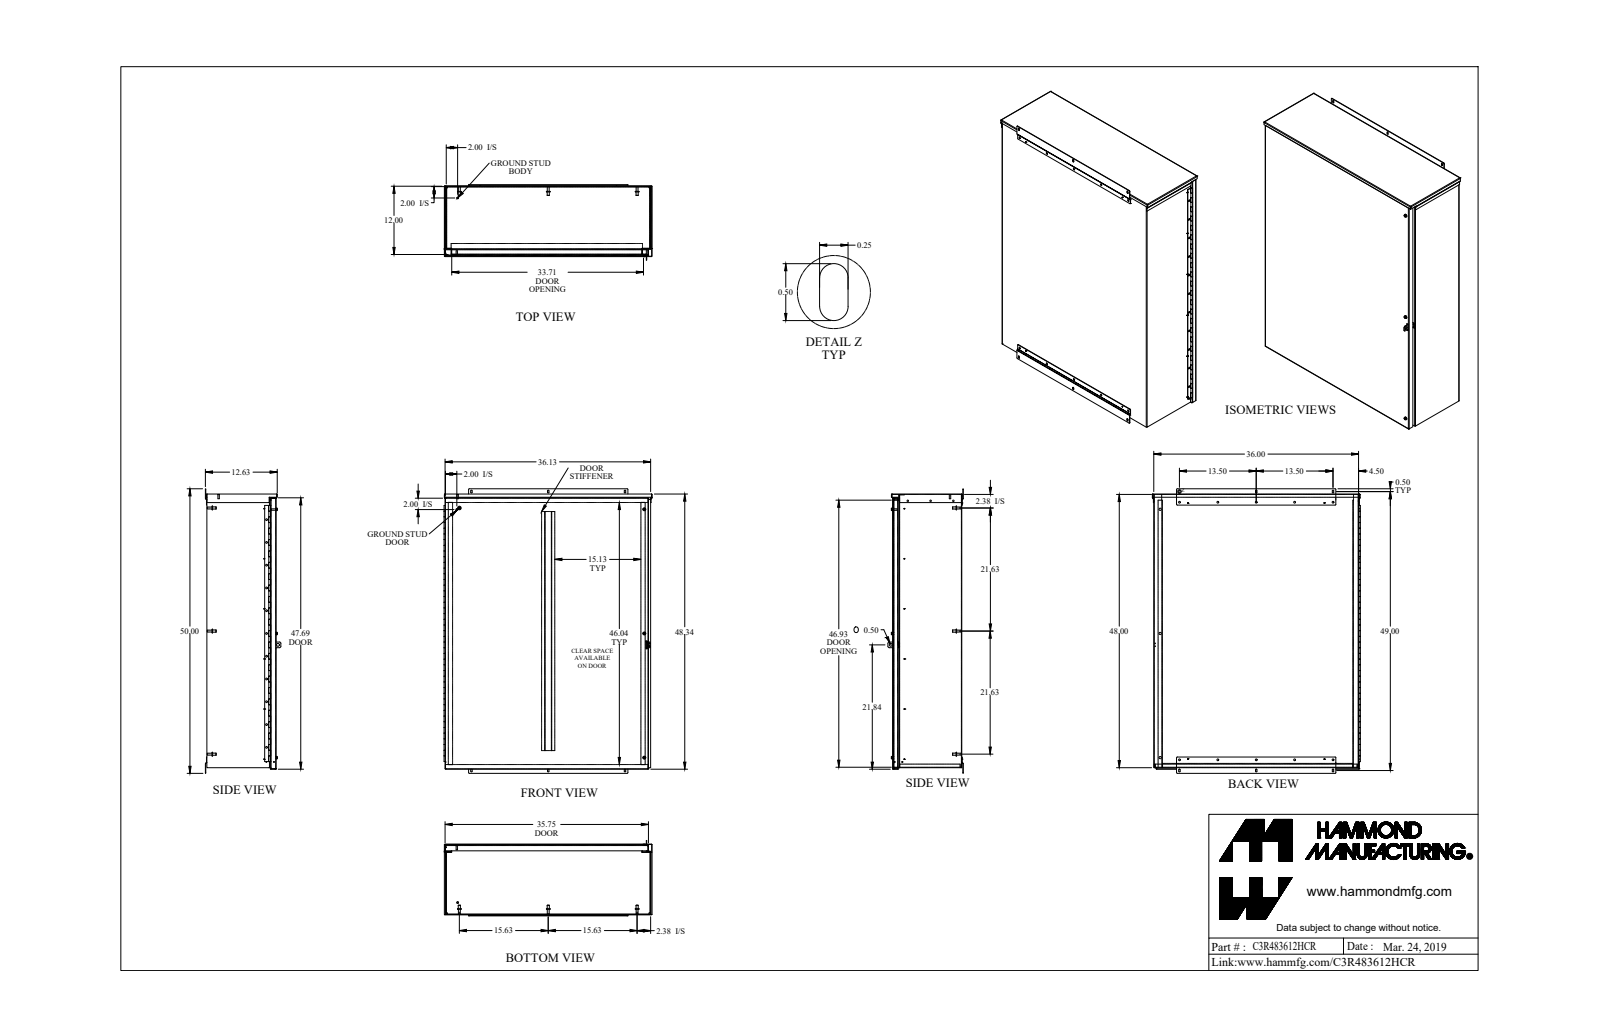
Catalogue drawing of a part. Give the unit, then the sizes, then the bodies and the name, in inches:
Units: inches
Overall size (bounding box): 50 × 36.571 × 13.26
Round holes (diameter × count): ⌀0.304 ×11, ⌀0.312 ×10, ⌀0.14 ×4, ⌀0.26 ×4, ⌀0.313 ×4, ⌀0.25 ×3, ⌀0.266 ×3, ⌀0.28 ×3, ⌀0.29 ×3, ⌀0.397 ×3, ⌀0.137 ×2, ⌀0.188 ×1
Round bosses / shafts (diameter × count): ⌀0.131 ×12, ⌀0.65 ×8, ⌀0.375 ×8, ⌀0.33 ×8, ⌀0.51 ×4, ⌀0.244 ×4, ⌀0.187 ×4, ⌀0.5 ×3
Partial cylindrical surfaces — rounded edges, fillets, slot ends (radius × count): R0.036 ×39, R0.108 ×39, R0.125 ×24, R0.171 ×4, R0.25 ×2
Main face-to-face distances: 0.072, 12.1, 12.028, 12.172, 35.928, 48, 36, 35.856, 47.928, 48.072
Hole centre spacings: 4, 8, 6.75, 12, 16, 24, 13.5, 20
Volume: 491.9 in³ · Surface area: 13 430 in²
Bodies: 43 solids, 1314 faces (671 planar, 551 cylindrical, 92 other)
Part name (STEP PRODUCT): C3R483612HCR_Default
STEP written by: SolidWorks 2019 (CONFIG_CONTROL_DESIGN)
